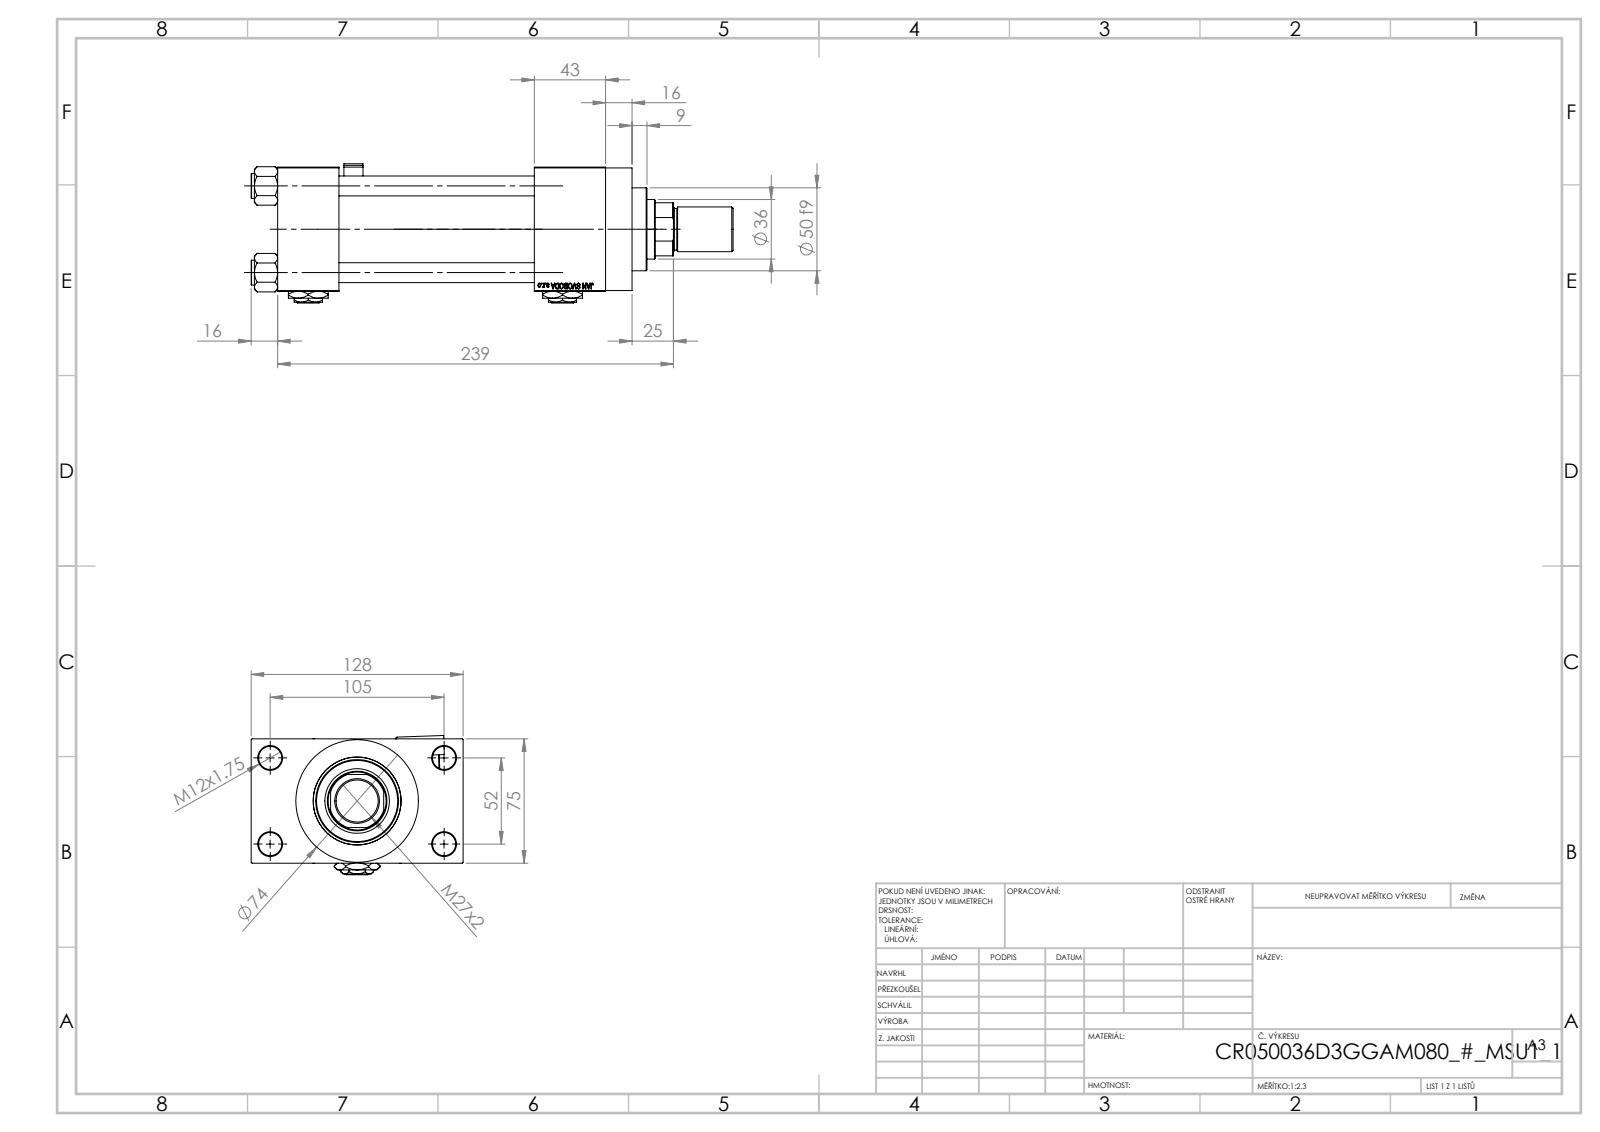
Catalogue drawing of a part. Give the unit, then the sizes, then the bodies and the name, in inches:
Units: inches
Overall size (bounding box): 11.457 × 5.039 × 3.308
Round holes (diameter × count): ⌀0.472 ×4, ⌀0.551 ×4, ⌀0.276 ×2, ⌀0.825 ×2, ⌀1.181 ×2, ⌀1.004 ×1, ⌀1.417 ×1, ⌀1.535 ×1, ⌀1.614 ×1, ⌀2.087 ×1
Round bosses / shafts (diameter × count): ⌀0.591 ×4, ⌀2.913 ×1, ⌀2.205 ×1, ⌀1.969 ×1, ⌀1.063 ×1, ⌀0.984 ×1, ⌀0.236 ×1
Partial cylindrical surfaces — rounded edges, fillets, slot ends (radius × count): R0.02 ×24, R0.039 ×1, R0.098 ×1, R0.157 ×1, R0.689 ×1
Main face-to-face distances: 2.953, 4.646, 1.457, 6.102, 1.043, 3.996, 1.693, 7.795, 6.339, 0.63
Hole centre spacings: 1.037, 1.456, 2.059, 2.3, 2.307, 3.096, 3.715, 2.047
Volume: 59.87 in³ · Surface area: 347.6 in²
Bodies: 15 solids, 1296 faces (578 planar, 134 cylindrical, 584 other)
Part name (STEP PRODUCT): NUT_M5_D; V215CR_D_Body; V215CR_D_TYCINKA; V215CR_MSU (+4 more)
STEP written by: SolidWorks 2019 (CONFIG_CONTROL_DESIGN)
